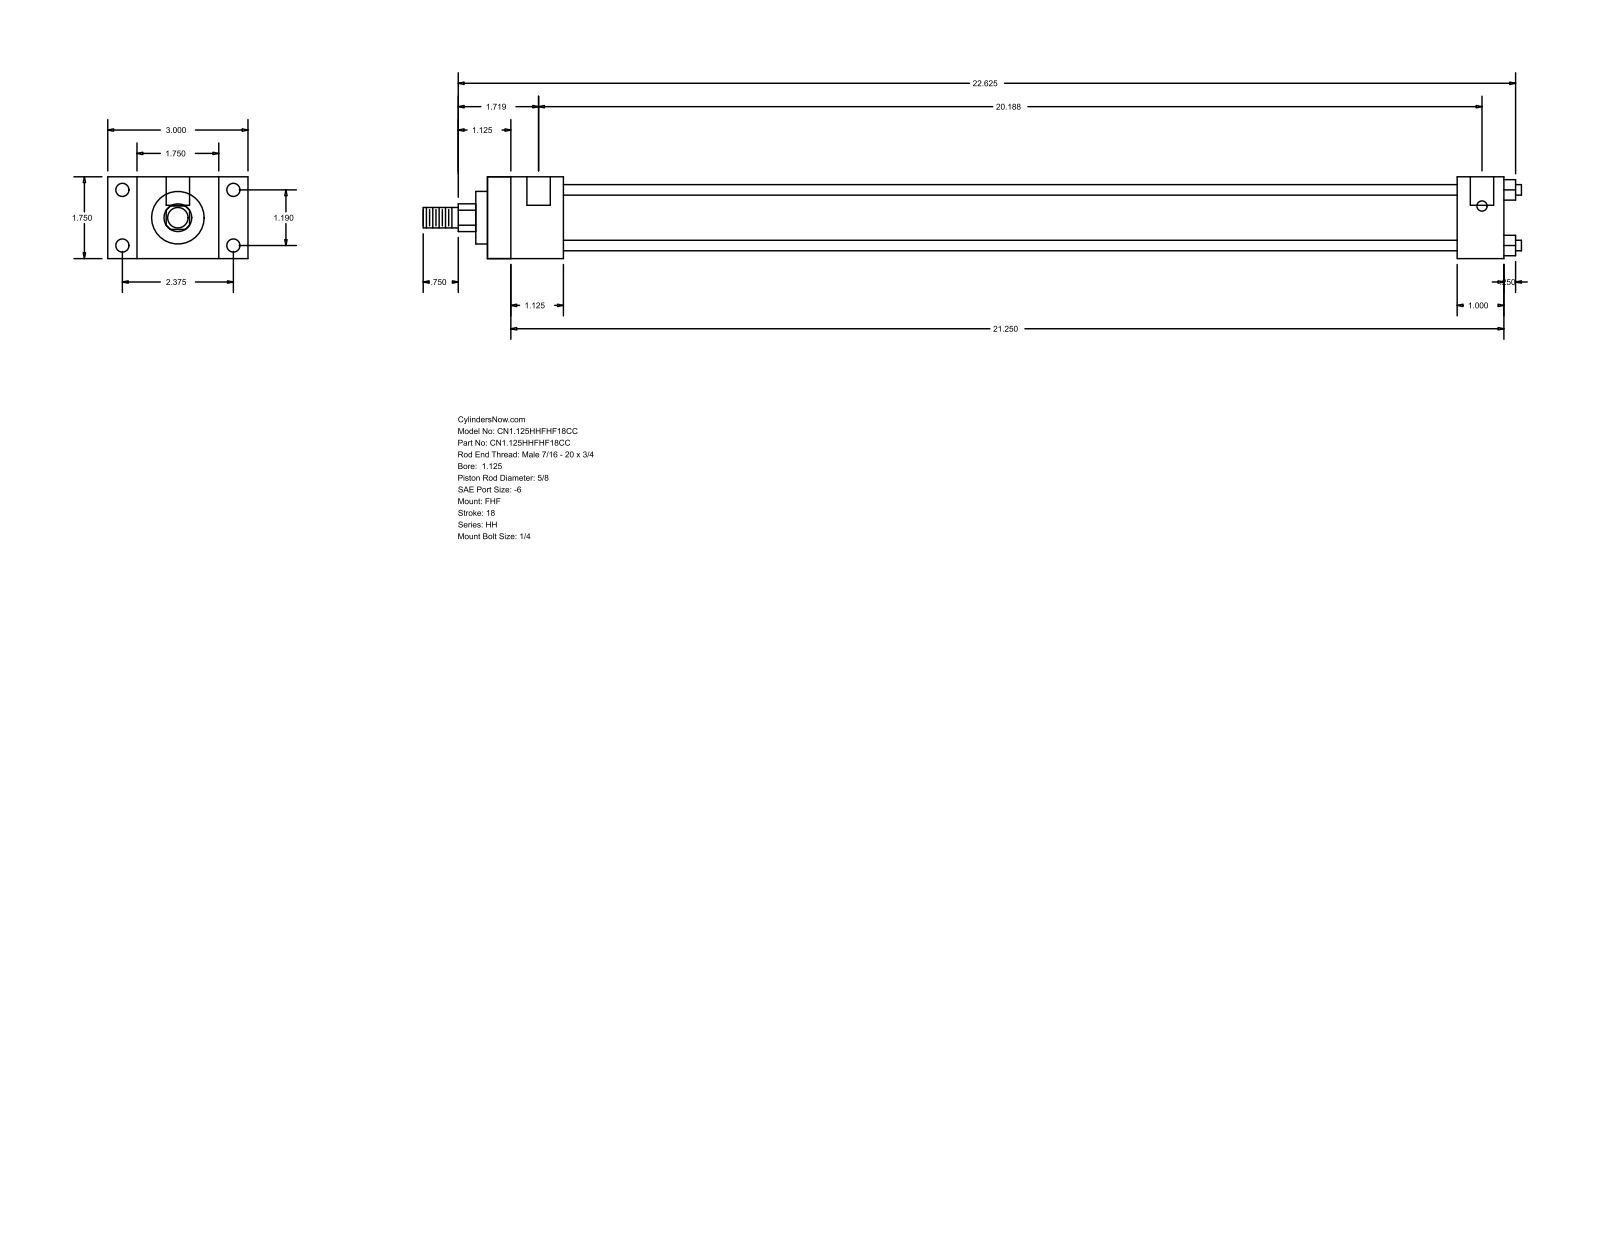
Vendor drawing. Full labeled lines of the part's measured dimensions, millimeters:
Part name (STEP PRODUCT): HH_FHF__0112_0.625
STEP written by: GSSL Pune (CONFIG_CONTROL_DESIGN)
Units: millimetres
Bodies: 0 solids, 88 faces (60 planar, 28 cylindrical, 0 other)
Overall size (bounding box): 596.9 × 76.2 × 44.45
Round holes (diameter × count): ⌀5.56 ×4, ⌀7.14 ×4, ⌀12.7 ×2
Round bosses / shafts (diameter × count): ⌀5.71 ×4, ⌀34.92 ×1, ⌀28.57 ×1, ⌀15.88 ×1, ⌀11.11 ×1
Partial cylindrical surfaces — rounded edges, fillets, slot ends (radius × count): R7.54 ×1
Main face-to-face distances: 44.46, 15.87, 60.33, 41.27, 76.2, 552.45, 511.18, 527.04, 485.77, 25.41
Hole centre spacings: 30.22, 60.32, 67.47, 509.59, 3.17, 512.76
